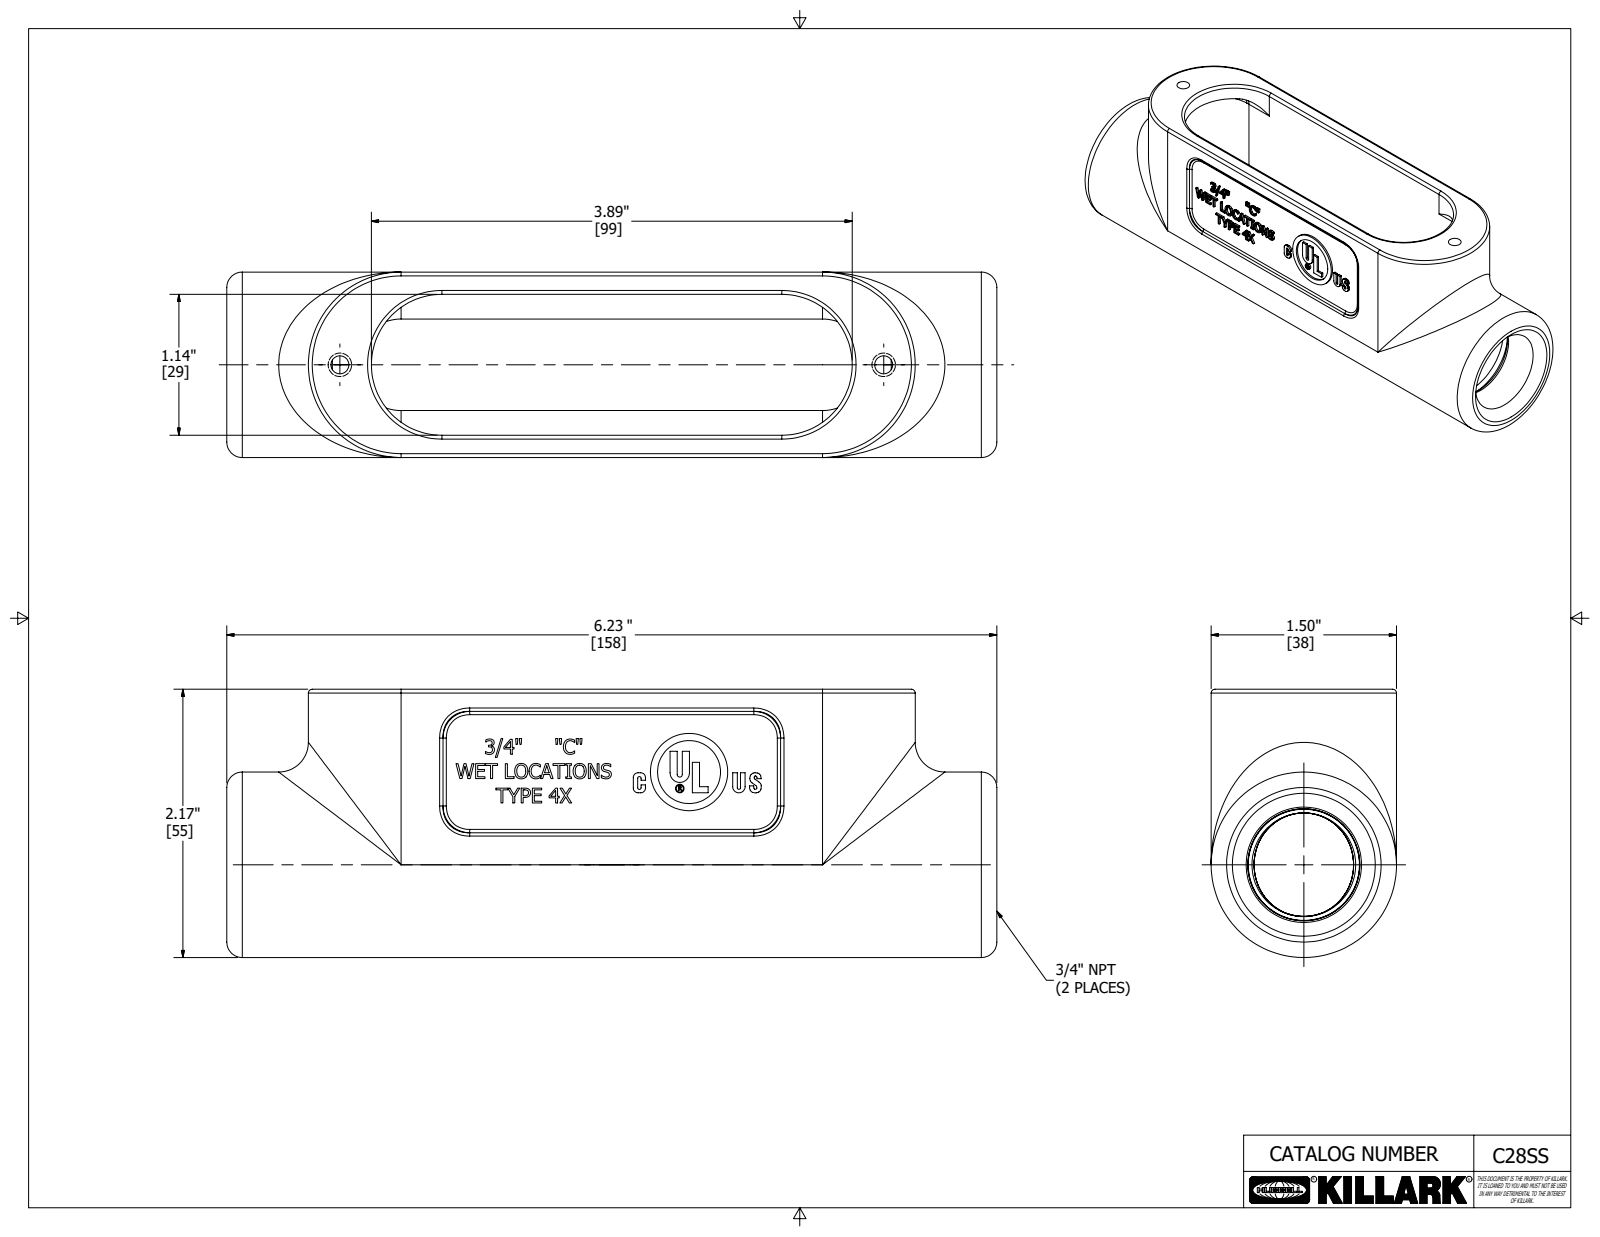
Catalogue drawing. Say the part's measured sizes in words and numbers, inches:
The part is named "C28SS". Its 3-D file was written by "Autodesk Inventor 2020 (AUTOMOTIVE_DESIGN)". It is 1 solid with 529 faces: 306 planar, 78 cylindrical and 145 other. Overall it measures 6.23 by 2.17 by 1.5 inches. Its volume is 5.76 cubic inches and its surface area 67.08 square inches. Round holes: 2 of diameter 0.145, 1 of diameter 0.058, 1 of diameter 0.509, 1 of diameter 1.055. Round bosses or shafts: 1 of diameter 1.5, 1 of diameter 0.625, 1 of diameter 0.069. Partial cylindrical surfaces (rounded edges, fillets, slot ends): 13 of radius 0.031, 4 of radius 0.038, 4 of radius 0.25, 4 of radius 0.57, 2 of radius 0.013, 2 of radius 0.013, 2 of radius 0.125, 2 of radius 0.2. The main face-to-face distances are 0.18, 1.32, 1.14, 0.149, 1.289, 1.469, 1.99, 0.031, 1.5, 1.81. The hole center spacings are 0.153, 4.4.
